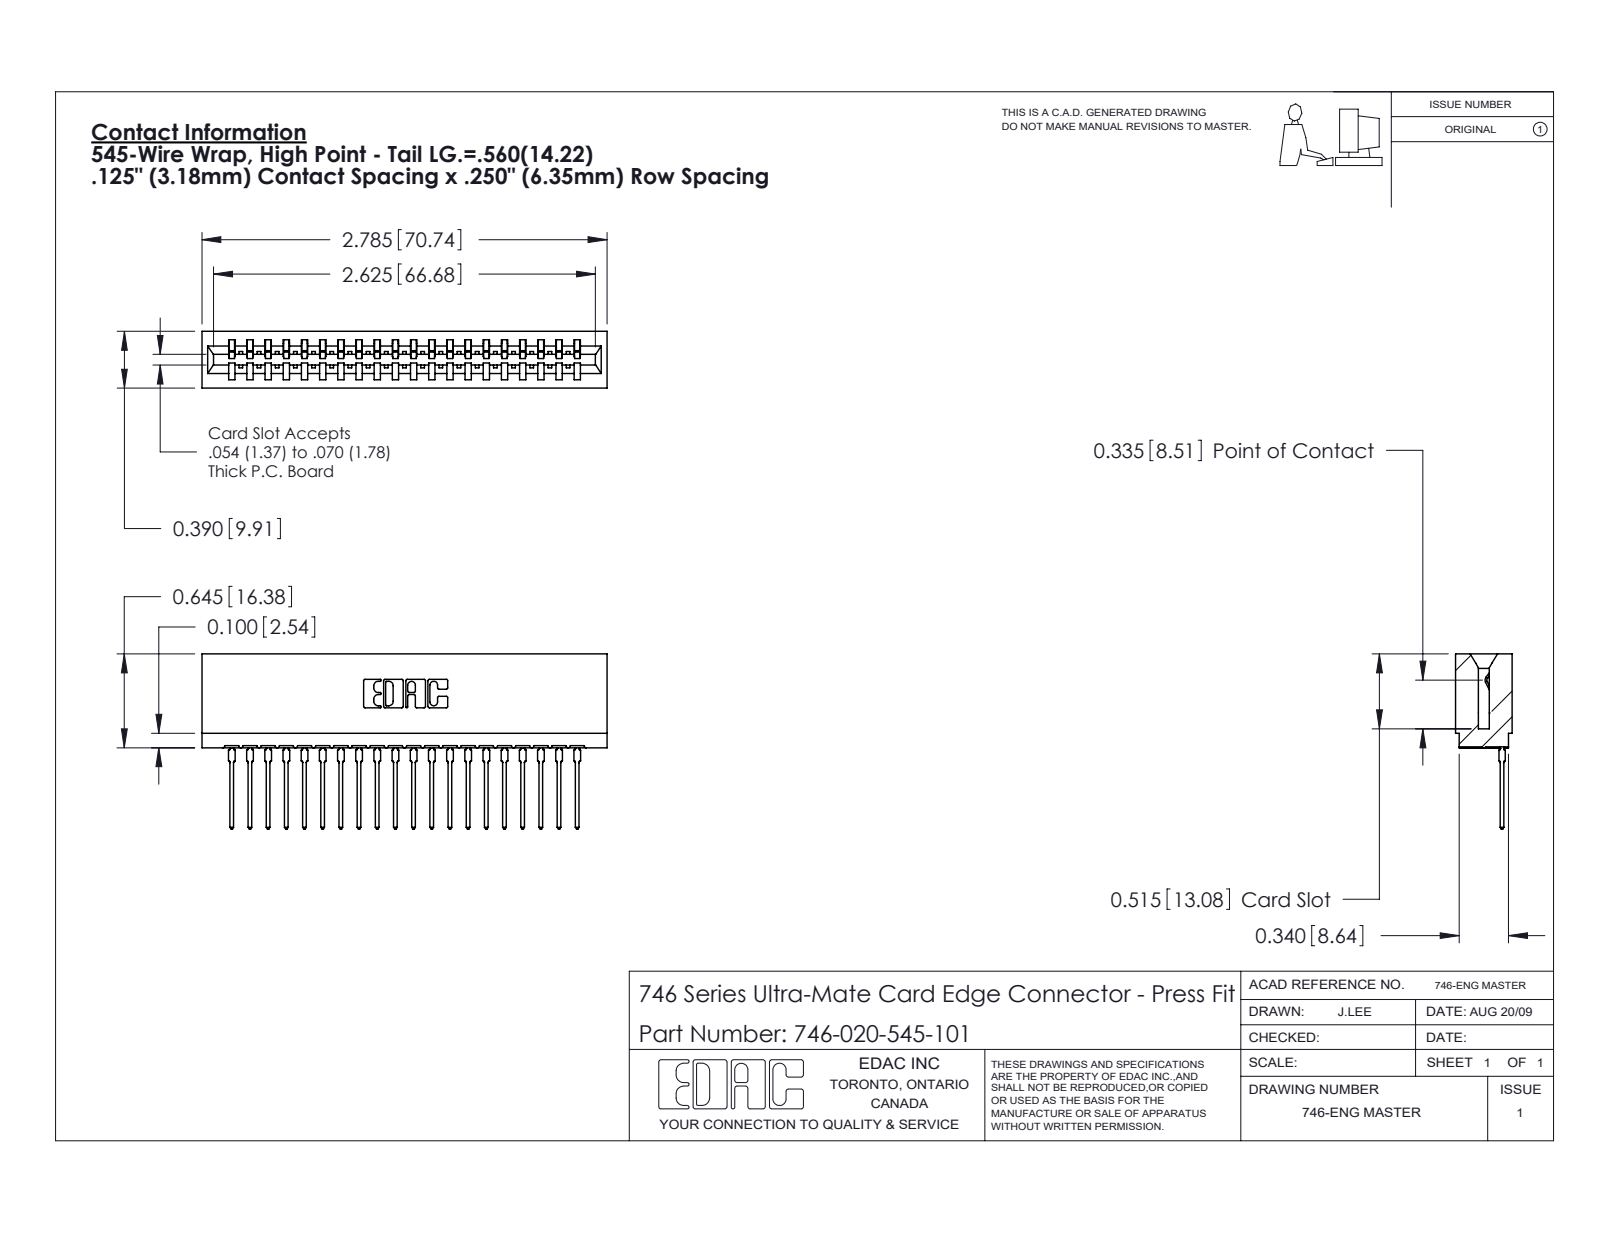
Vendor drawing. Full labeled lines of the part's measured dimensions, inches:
Part name (STEP PRODUCT): 746-020-545-101; 746-292-001_545; 746 Part_.515 Slot Depth - 01
STEP written by: SolidWorks 2020 (CONFIG_CONTROL_DESIGN)
Units: inches
Bodies: 21 solids, 2257 faces (1315 planar, 422 cylindrical, 520 other)
Overall size (bounding box): 2.785 × 1.204 × 0.39
Volume: 0.463 in³ · Surface area: 17.32 in²
Partial cylindrical surfaces — rounded edges, fillets, slot ends (radius × count): R0.021 ×40, R0.01 ×22, R0.015 ×21, R0.007 ×6, R0.031 ×6, R0.005 ×4, R0.011 ×4, R0.026 ×3
Main face-to-face distances: 0.25, 0.057, 0.333, 0.39, 0.5, 0.025, 0.307, 0.083, 0.375, 0.125
